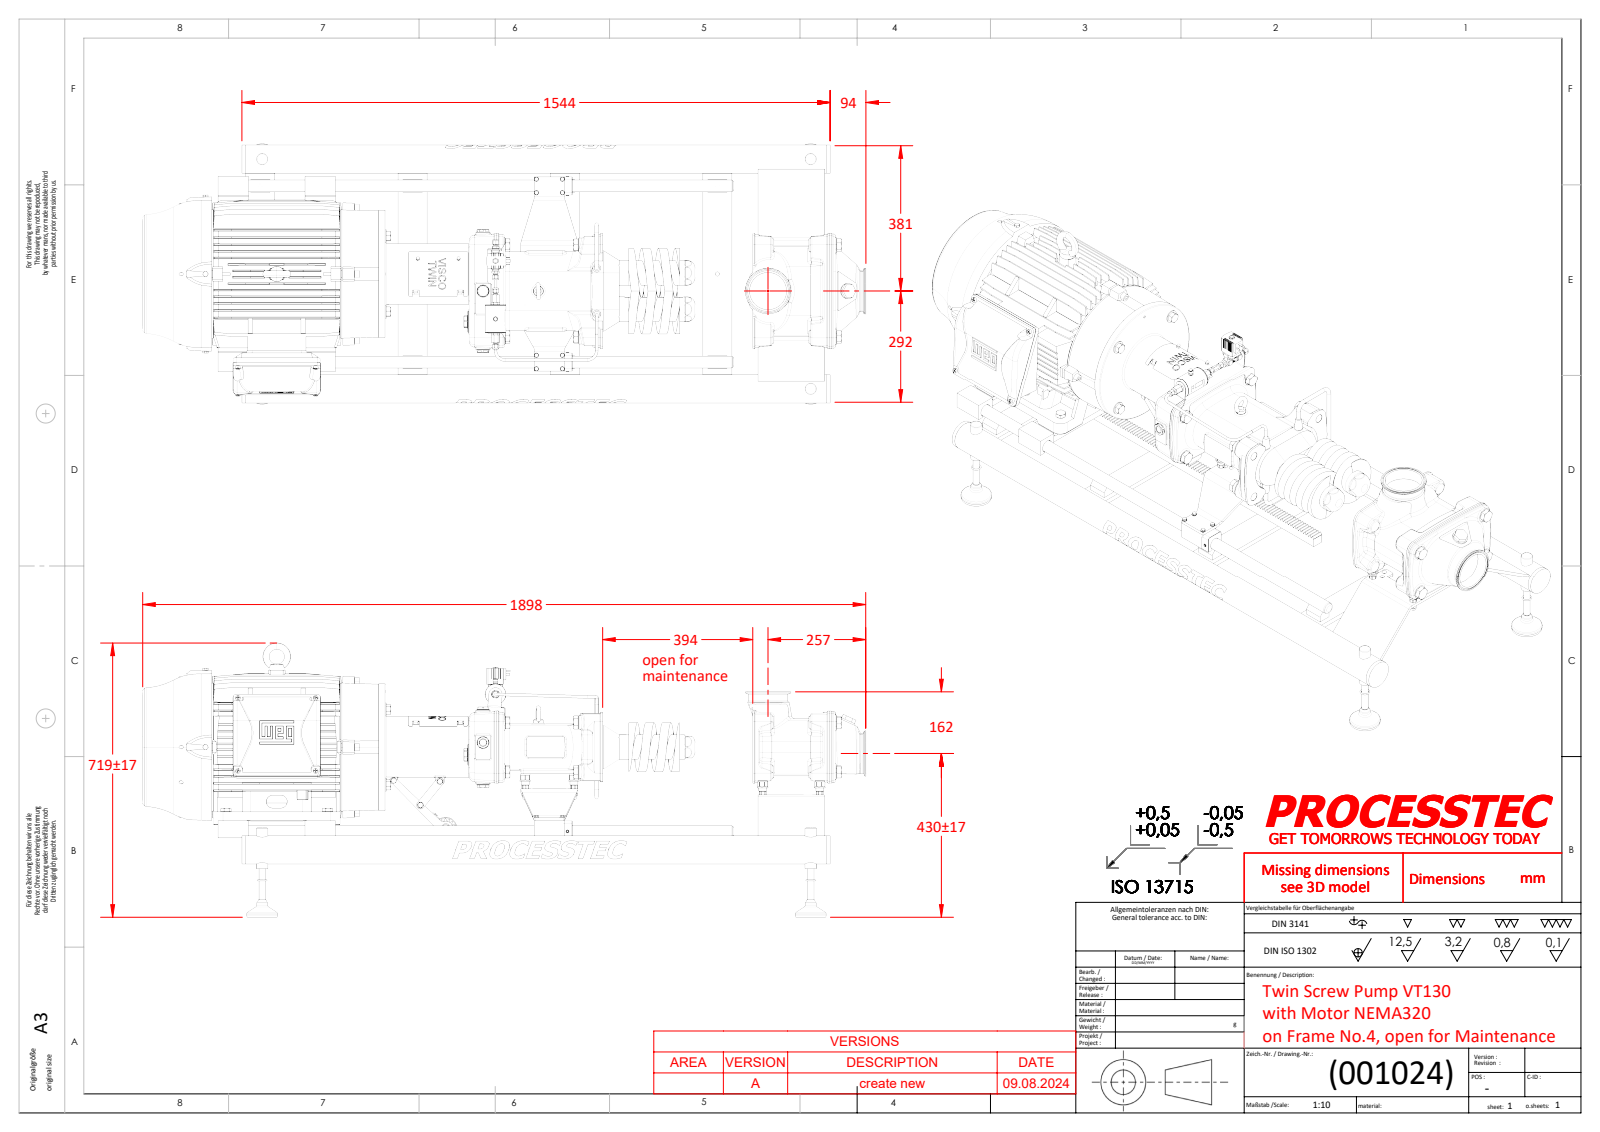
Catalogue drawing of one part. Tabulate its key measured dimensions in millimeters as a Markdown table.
| quantity | value |
| --- | --- |
| part name | Twin Screw Pump VT130 on F4 with NEMA320 open for maintenance - 001024 |
| STEP written by | SolidWorks 2023 (AUTOMOTIVE_DESIGN) |
| units | millimeters |
| bodies | 0 solids, 14036 faces (4658 planar, 3713 cylindrical, 5665 other) |
| overall size | 1898.41 × 719.46 × 680.5 |
| round holes (diameter × count) | 8.5 × 24, 5 × 19, 14 × 14, 13 × 13, 17.5 × 13, 6.8 × 12, 4.1 × 11, 8 × 9, 10.5 × 9, 6.4 × 8, 10.1 × 8, 10.25 × 8 |
| round bosses / shafts (diameter × count) | 10 × 33, 6 × 19, 24 × 17, 20 × 16, 8 × 13, 18.5 × 12, 17 × 11, 16 × 11 |
| partial cylindrical surfaces (radius × count) | 2.98 × 188, 3 × 81, 1.5 × 54, 6 × 48, 2 × 39, 9 × 30, 8 × 27, 4 × 19 |
| main face-to-face distances | 342.3, 12.7, 8, 747.8, 405.5, 444.3, 102, 303.5, 1178.5, 72.7 |
| hole center spacings | 461.41, 400, 129.3, 230, 832.41, 55, 609.59, 800 |
